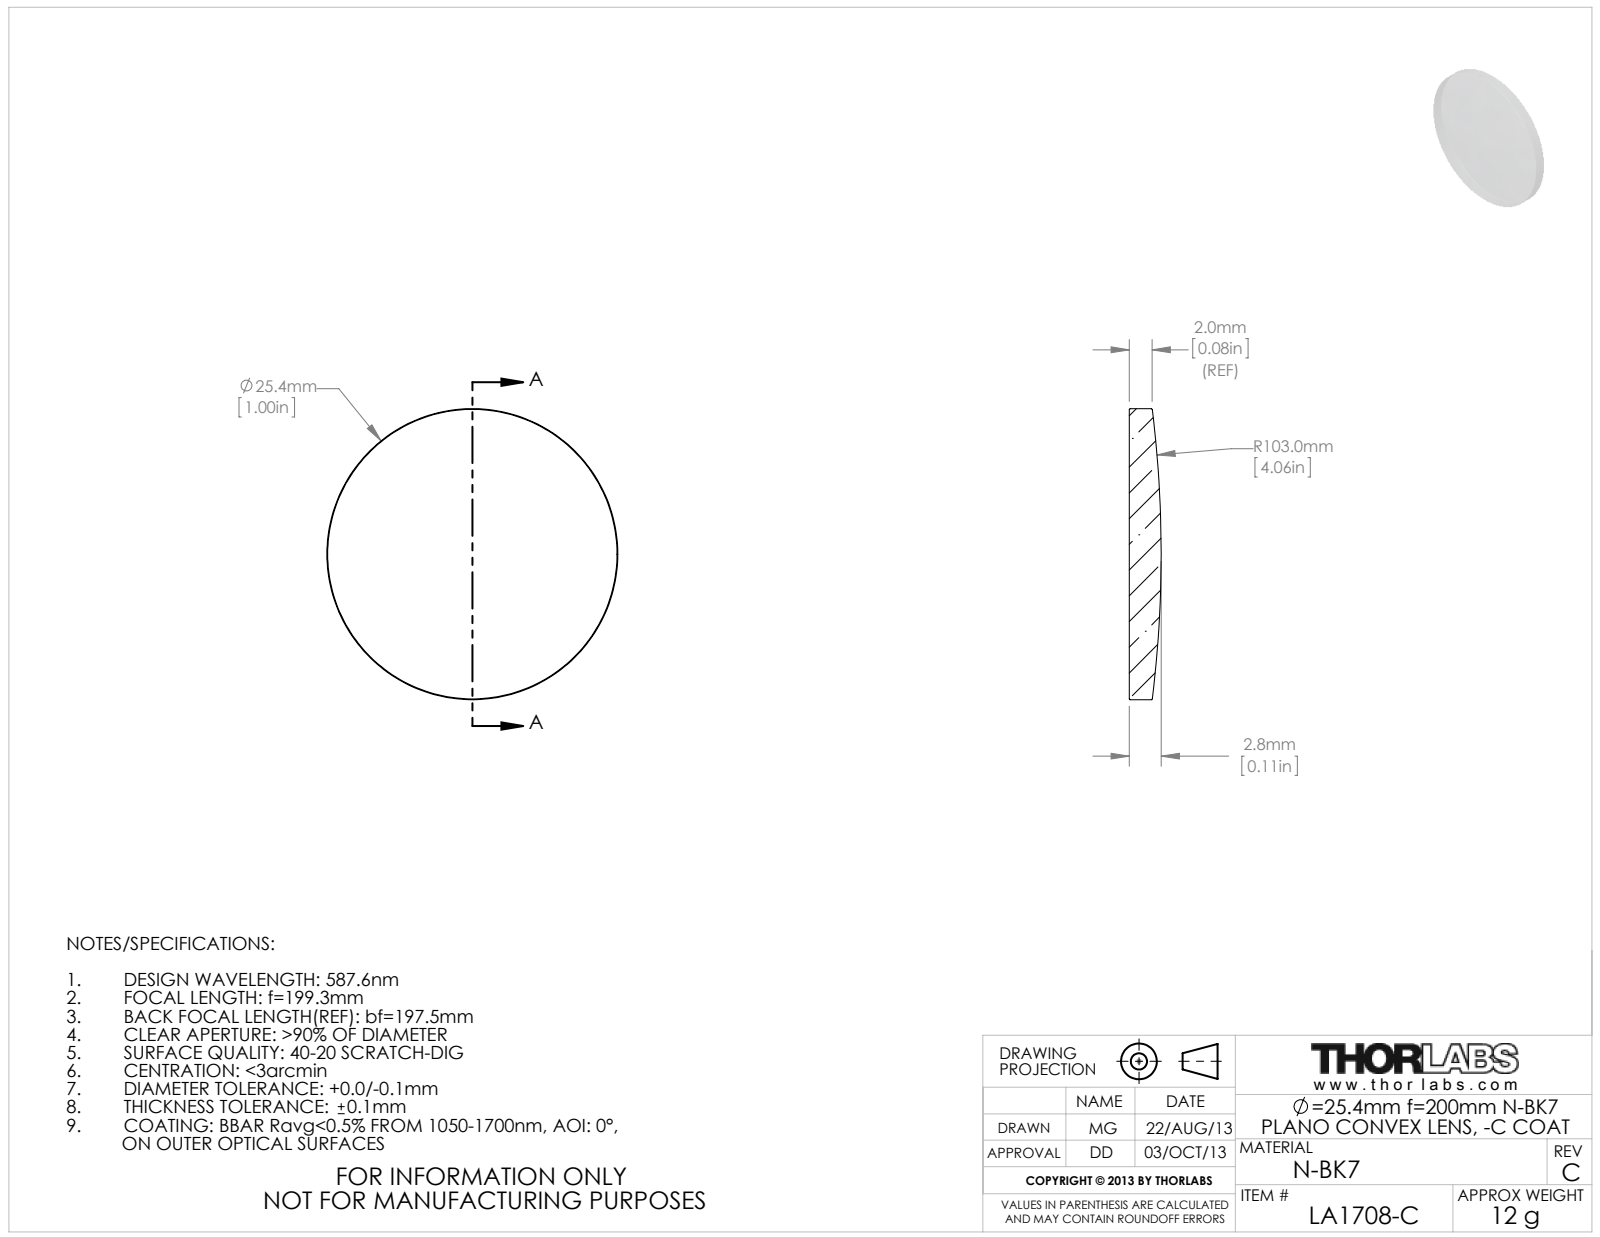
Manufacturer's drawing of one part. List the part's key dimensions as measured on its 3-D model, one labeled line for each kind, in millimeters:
Part name (STEP PRODUCT): 4588-E0W
STEP written by: SolidWorks 2009 (AUTOMOTIVE_DESIGN)
Units: millimetres
Bodies: 1 solid, 5 faces (1 planar, 2 cylindrical, 2 other)
Overall size (bounding box): 25.4 × 25.4 × 2.78
Volume: 1 210 mm³ · Surface area: 1 174 mm²
Round bosses / shafts (diameter × count): ⌀25.4 ×1
